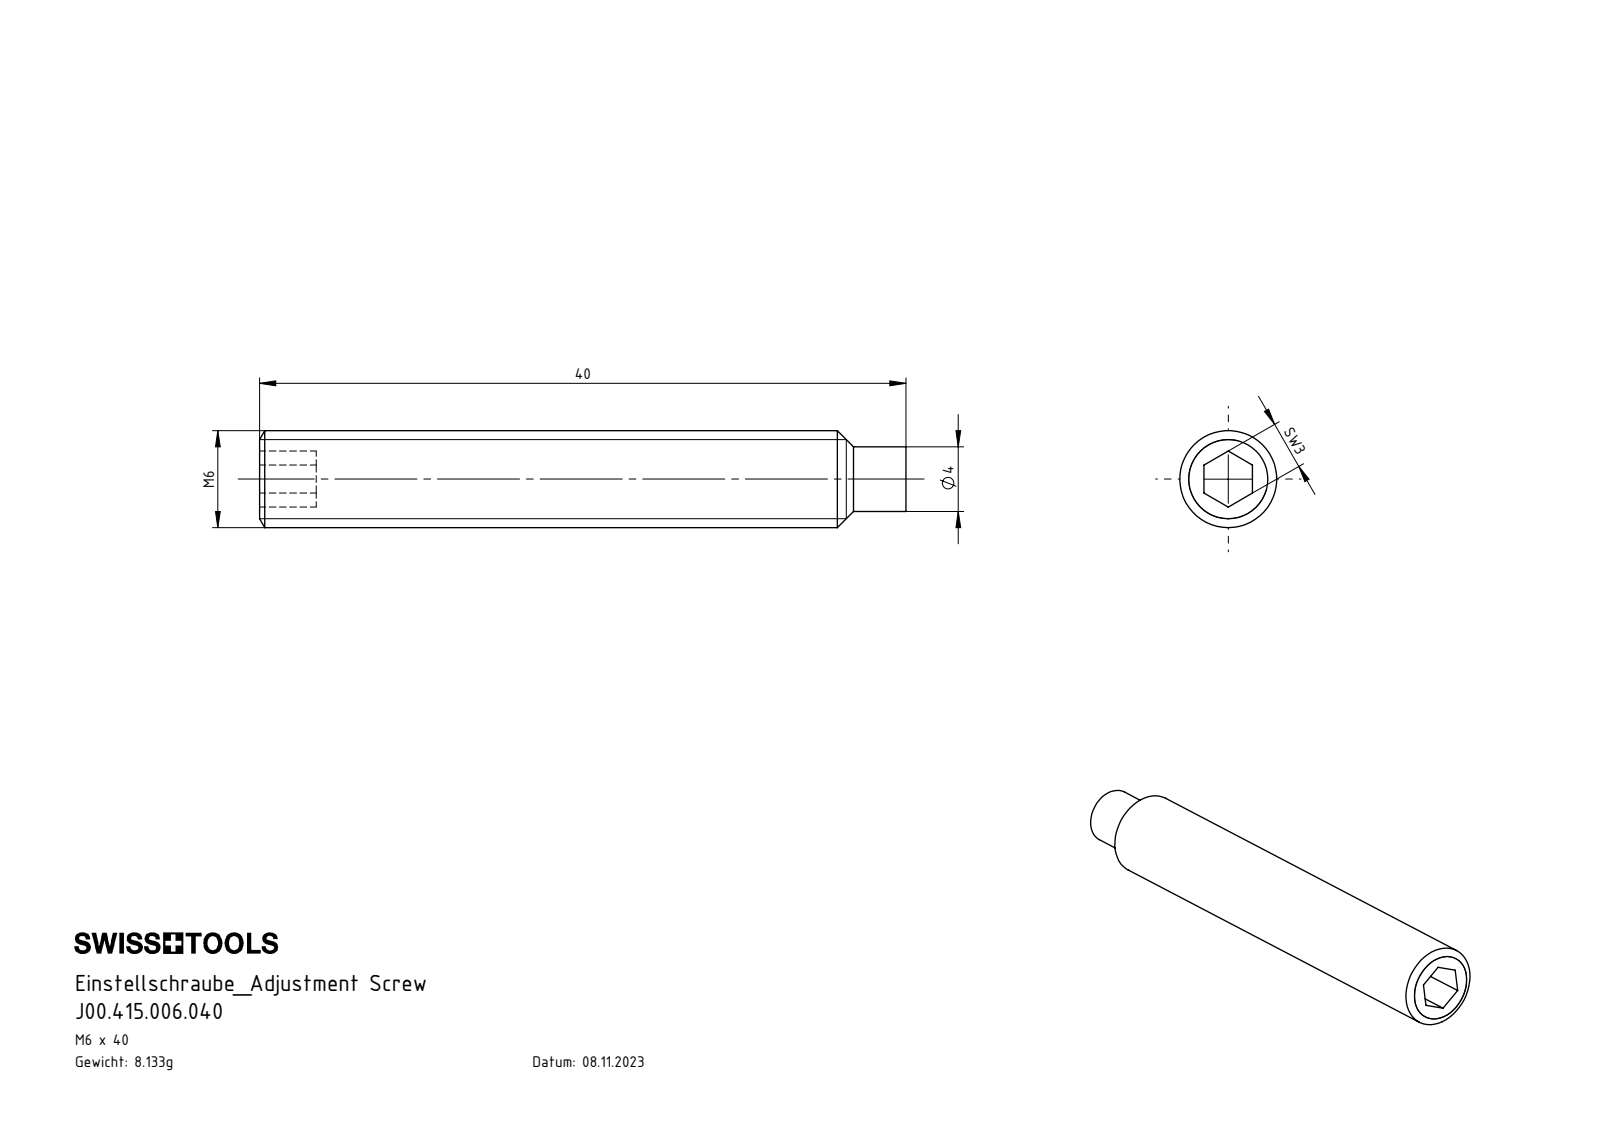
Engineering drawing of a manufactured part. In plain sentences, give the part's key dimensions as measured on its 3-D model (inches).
The part is named "J00.415.006.040". Its 3-D file was written by "SolidWorks 2022 (AUTOMOTIVE_DESIGN)". It is 1 solid with 17 faces: 9 planar, 4 cylindrical and 4 other. Overall it measures 1.575 by 0.236 by 0.236 inches. Its volume is 0.064 cubic inches and its surface area 1.26 square inches. Round bosses or shafts: 1 of diameter 0.236, 1 of diameter 0.157. The main face-to-face distances are 0.118, 1.575, 0.138, 1.437.
